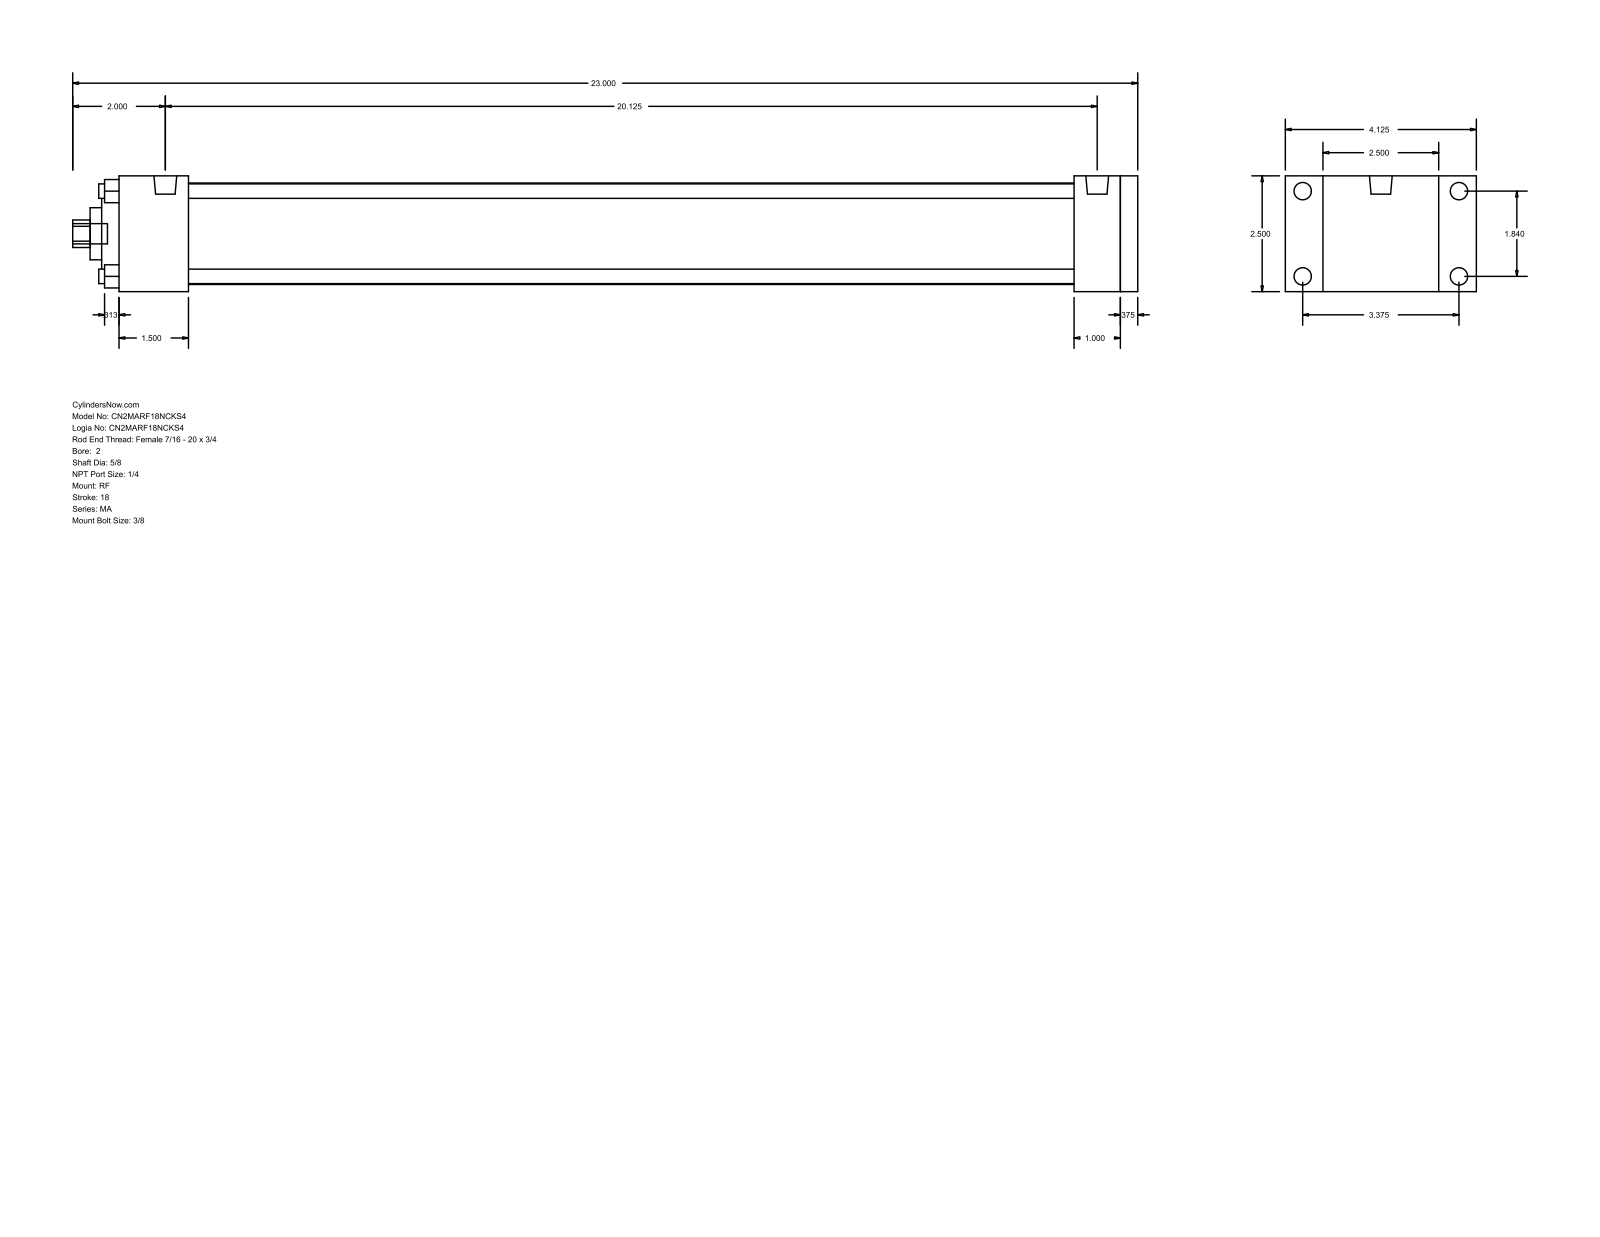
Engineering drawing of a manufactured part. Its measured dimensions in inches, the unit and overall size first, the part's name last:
Units: inches
Overall size (bounding box): 23 × 4.125 × 2.5
Round holes (diameter × count): ⌀0.313 ×4, ⌀0.625 ×1, ⌀1.125 ×1, ⌀2 ×1, ⌀2.19 ×1
Round bosses / shafts (diameter × count): ⌀0.375 ×4, ⌀0.313 ×4, ⌀0.492 ×2, ⌀0.437 ×1
Partial cylindrical surfaces — rounded edges, fillets, slot ends (radius × count): R0.297 ×1
Main face-to-face distances: 2.5, 0.375, 1, 1.5, 21.625, 0.375, 22, 22.375, 20.125, 20.5
Hole centre spacings: 1.301, 1.84, 2.602
Bodies: 0 solids, 94 faces (65 planar, 29 cylindrical, 0 other)
Part name (STEP PRODUCT): MA_RF__0200_0.625
STEP written by: GSSL Pune (CONFIG_CONTROL_DESIGN)
